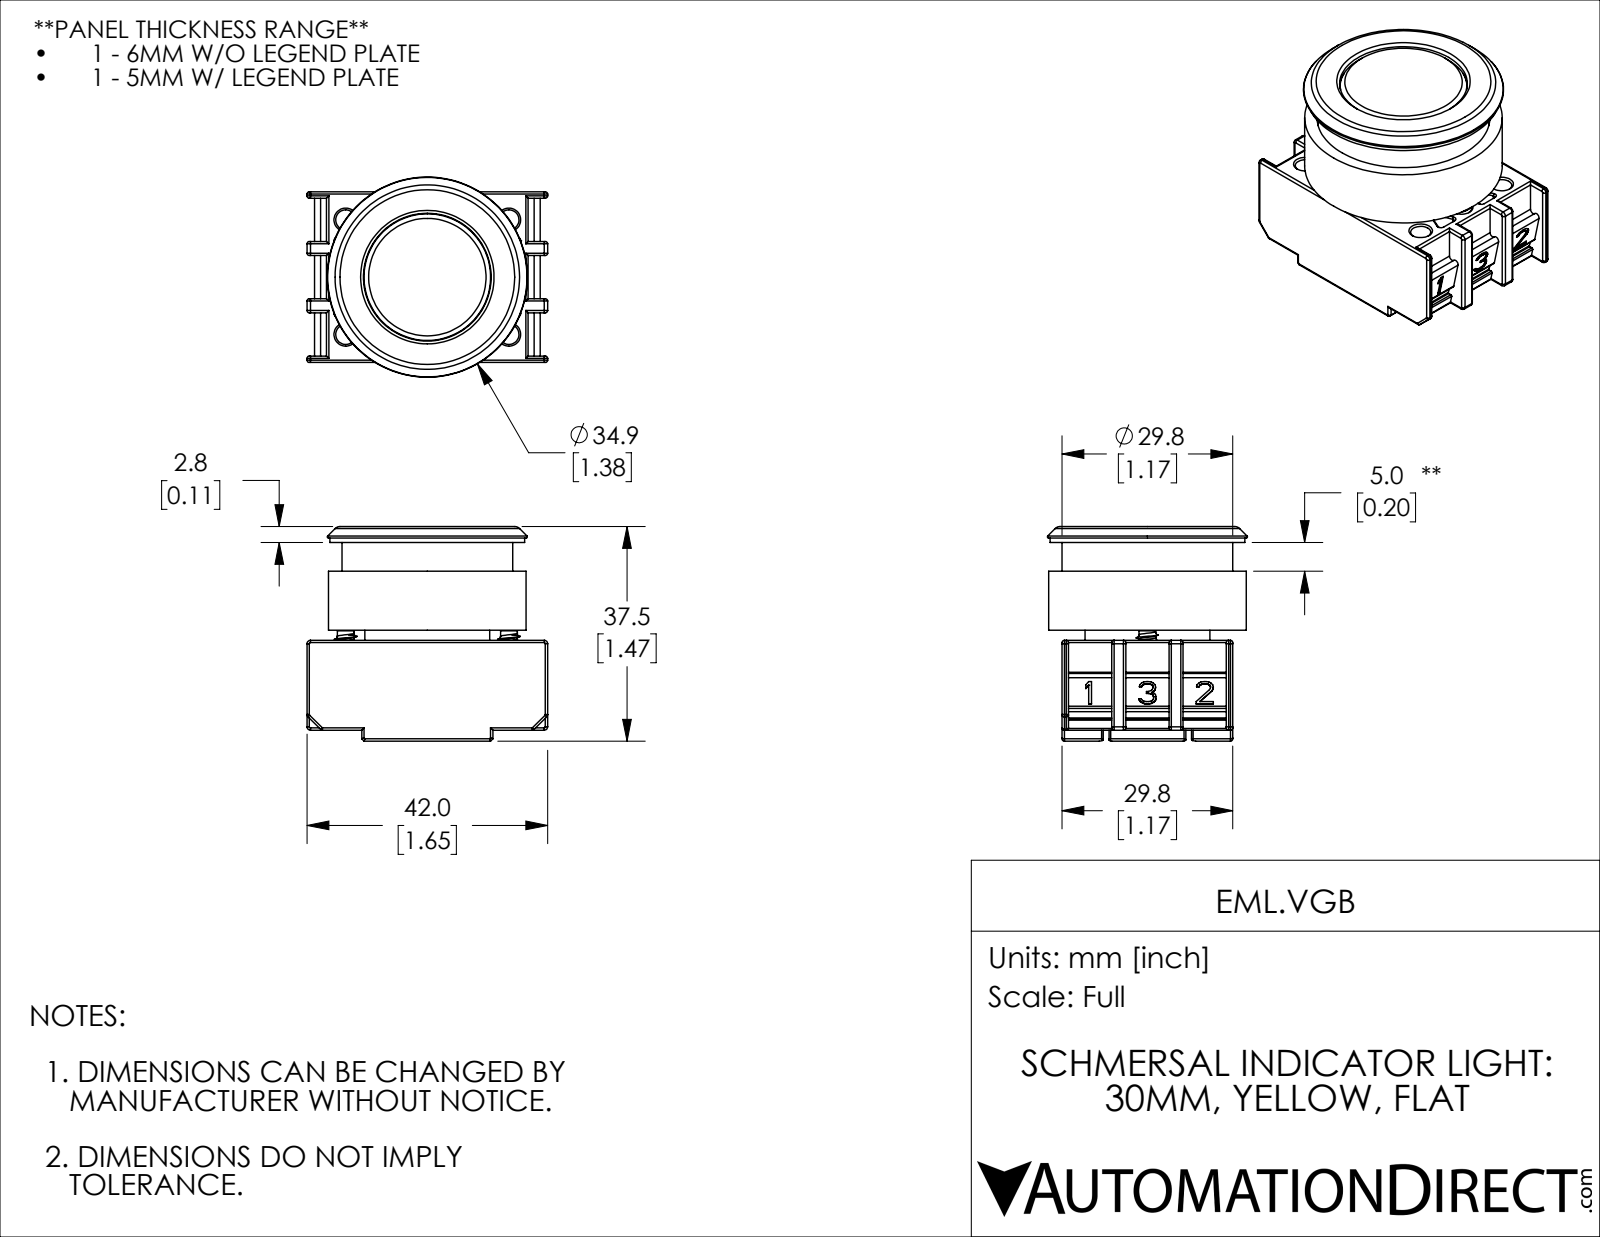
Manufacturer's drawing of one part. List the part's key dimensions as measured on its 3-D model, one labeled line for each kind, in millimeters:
Part name (STEP PRODUCT): EML.VGB
STEP written by: SolidWorks 2019 (CONFIG_CONTROL_DESIGN)
Units: millimetres
Bodies: 3 solids, 1372 faces (495 planar, 474 cylindrical, 403 other)
Overall size (bounding box): 42 × 37.45 × 34.93
Volume: 22 251 mm³ · Surface area: 21 607 mm²
Round holes (diameter × count): ⌀3.5 ×6, ⌀5.15 ×6, ⌀11 ×1, ⌀12.6 ×1, ⌀15 ×1, ⌀18 ×1, ⌀22.3 ×1, ⌀24.2 ×1, ⌀26 ×1, ⌀27 ×1, ⌀30.2 ×1
Round bosses / shafts (diameter × count): ⌀4.8 ×2, ⌀2.93 ×2, ⌀34.5 ×1, ⌀34 ×1, ⌀29.8 ×1, ⌀25.5 ×1, ⌀24 ×1, ⌀23.8 ×1
Partial cylindrical surfaces — rounded edges, fillets, slot ends (radius × count): R0.4 ×115, R0.3 ×48, R0.2 ×28, R0.6 ×8, R0.5 ×6, R0.1 ×2, R0.6 ×2, R0.8 ×2
Main face-to-face distances: 29.8, 14.7, 1.75, 16.45, 3.4, 10, 1.9, 19.35, 19.65, 17.9
Hole centre spacings: 10, 17.41, 30.2, 28.5, 14.25, 20, 34.82
